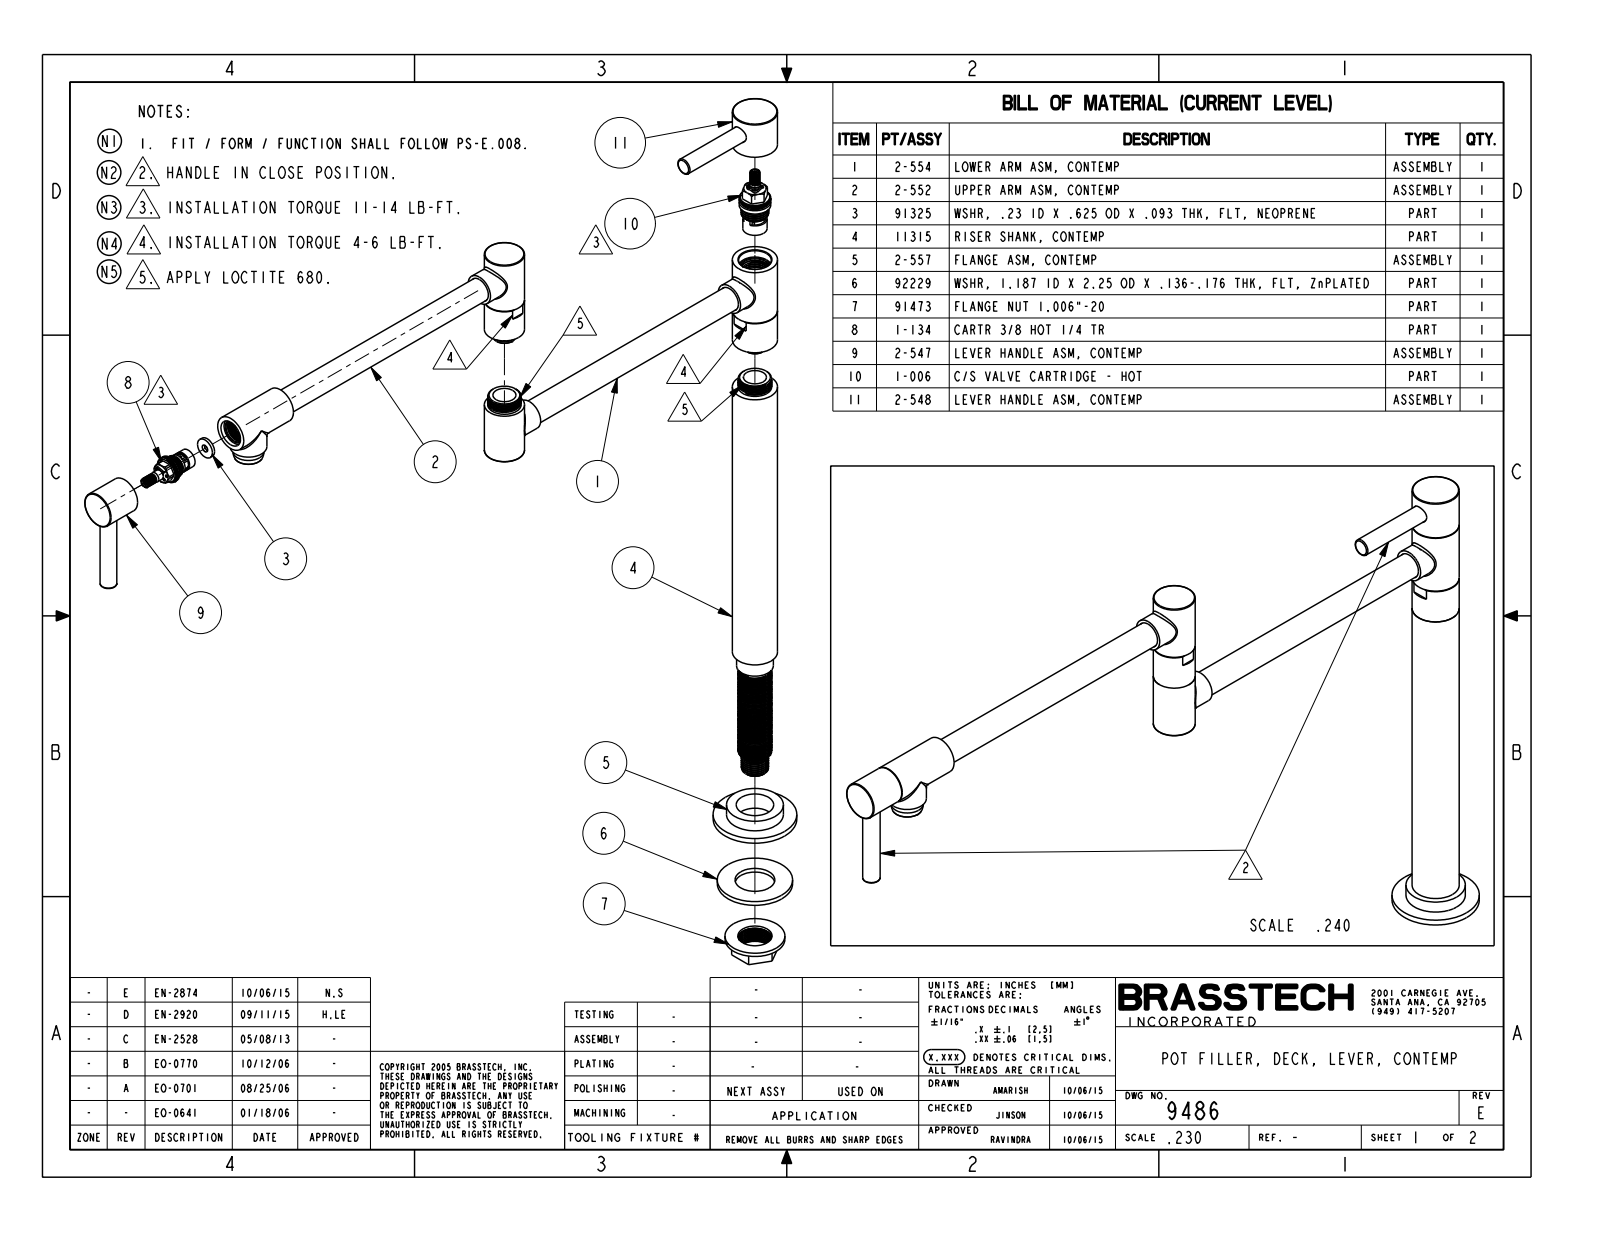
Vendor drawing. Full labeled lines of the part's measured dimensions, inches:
Part name (STEP PRODUCT): 11328; 11329; 11294; 11306 (+8 more)
STEP written by: PRO/ENGINEER BY PARAMETRIC TECHNOLOGY CORPORATION, 2009300 (CONFIG_CONTROL_DESIGN)
Units: inches
Bodies: 35 solids, 2230 faces (626 planar, 944 cylindrical, 660 other)
Overall size (bounding box): 24.57 × 19.559 × 2.5
Volume: 30.4 in³ · Surface area: 440.1 in²
Round holes (diameter × count): ⌀0.689 ×3, ⌀0.196 ×2, ⌀0.201 ×2, ⌀0.265 ×2, ⌀0.319 ×2, ⌀0.52 ×2, ⌀0.564 ×2, ⌀0.62 ×2, ⌀0.63 ×2, ⌀0.687 ×2, ⌀0.7 ×2, ⌀0.76 ×2
Round bosses / shafts (diameter × count): ⌀1.1 ×3, ⌀0.75 ×3, ⌀1 ×2, ⌀0.94 ×2, ⌀0.938 ×2, ⌀0.935 ×2, ⌀0.865 ×2, ⌀0.79 ×2
Partial cylindrical surfaces — rounded edges, fillets, slot ends (radius × count): R0.04 ×7, R0.08 ×6, R0.057 ×2, R0.063 ×2, R0.136 ×2, R0.145 ×2, R0.149 ×2, R0.3 ×2
Main face-to-face distances: 0.17, 0.52, 0.35, 14.37, 14.2, 13.85, 2.92, 1.08, 0.02, 1.87
Hole centre spacings: 0.06, 0.228, 1.26, 1.3, 1.39, 1.45, 1.6, 2.86
